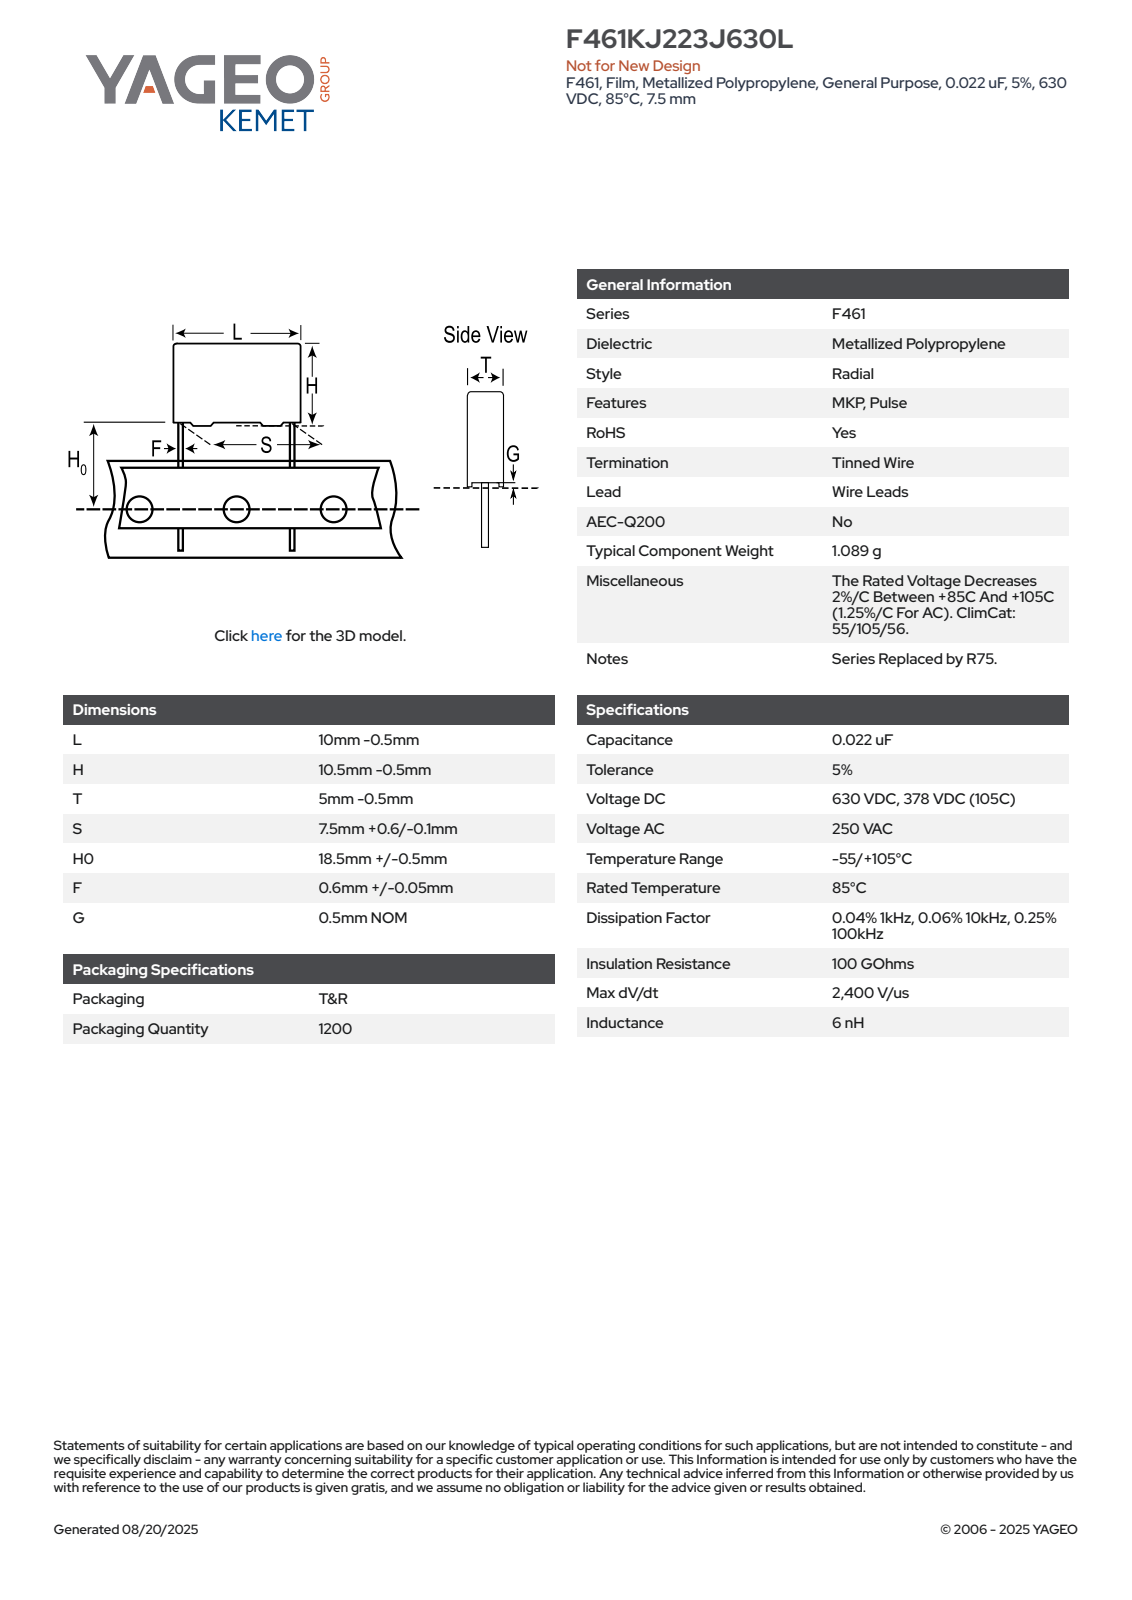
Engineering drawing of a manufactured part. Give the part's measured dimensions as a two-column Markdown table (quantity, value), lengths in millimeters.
| quantity | value |
| --- | --- |
| part name | CFR_RBG_10X10.5X5_L9.5H10T4.5S7.5H019F0.65G0.5 |
| STEP written by | SolidWorks 2014 (AUTOMOTIVE_DESIGN) |
| units | millimeters |
| bodies | 4 solids, 89 faces (81 planar, 8 cylindrical, 0 other) |
| overall size | 29 × 9.5 × 4.5 |
| volume | 418 mm³ |
| surface area | 442 mm² |
| round bosses / shafts (diameter × count) | 0.65 × 2 |
| partial cylindrical surfaces (radius × count) | 0.5 × 4 |
| main face-to-face distances | 4.5, 9.5, 4.24, 3.98, 0.5, 10, 19, 19.5, 29, 4.05 |
